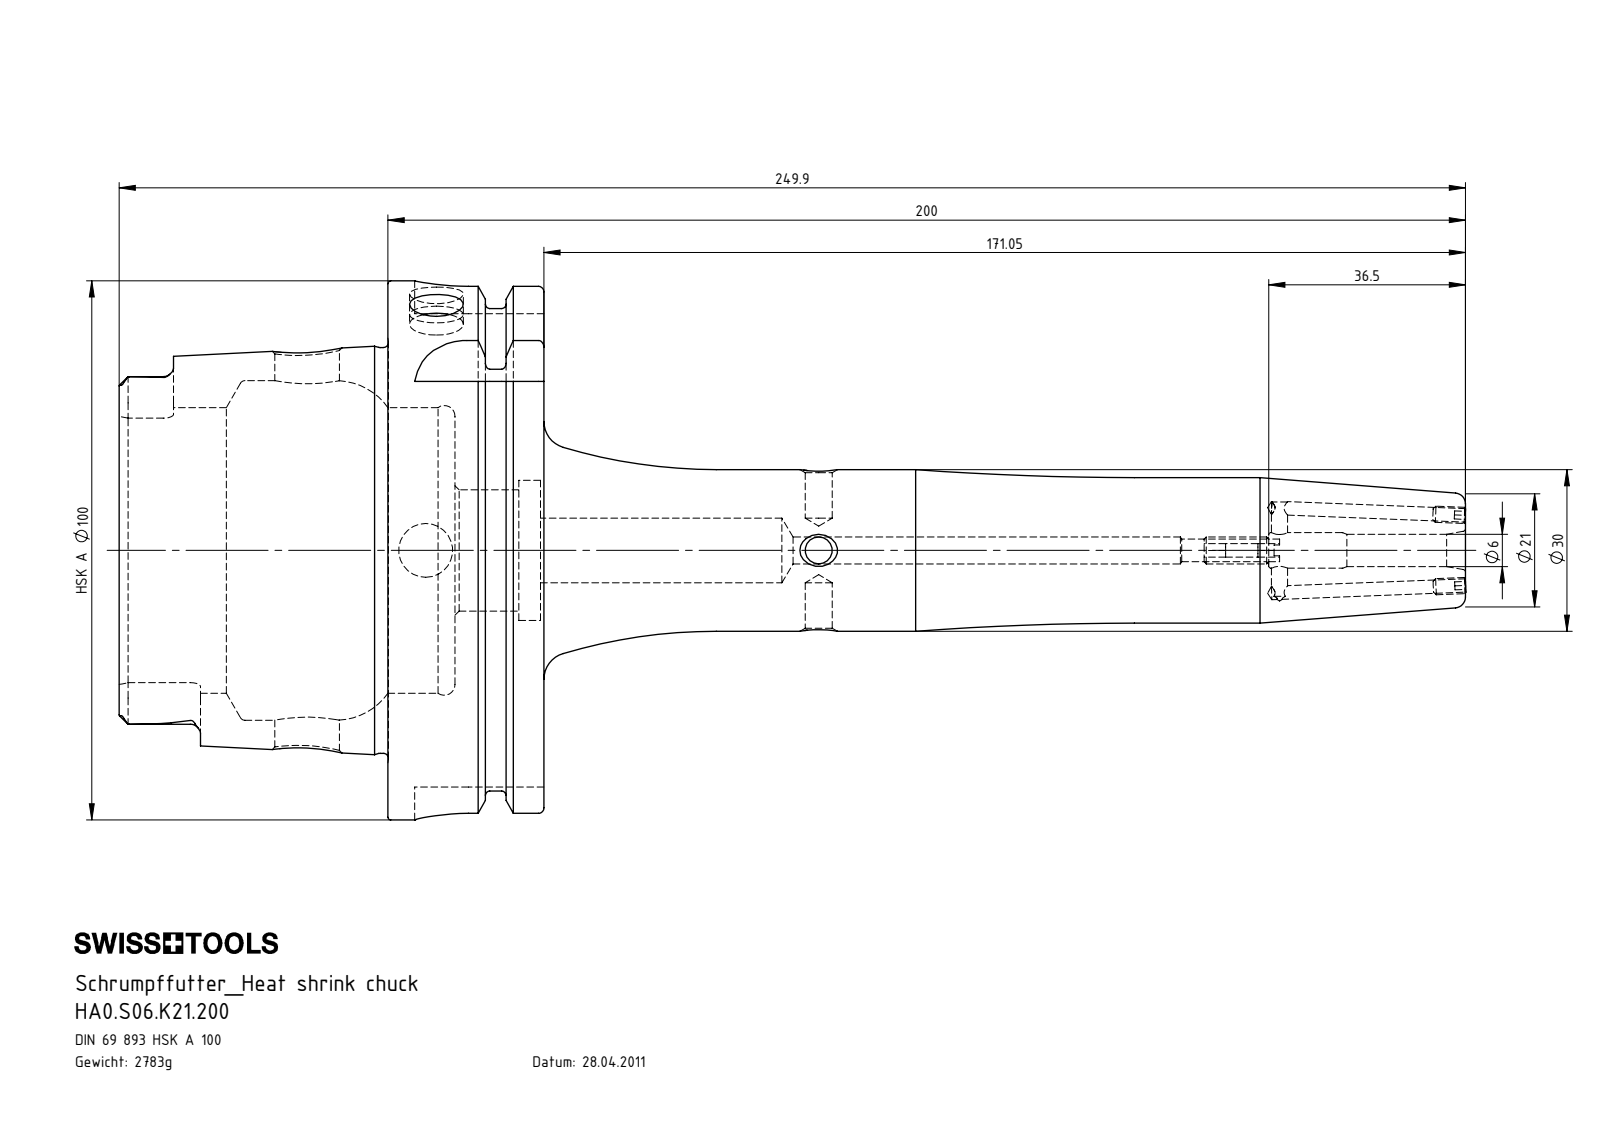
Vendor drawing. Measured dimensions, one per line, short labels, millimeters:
name: ERU-CJ2.001.006; HA0.S06.K21.200; ERU-AN1.K01.014_A; HA0-S06.K21.200_C_Fertigbearbeitung
written by: SolidWorks 2017 (CONFIG_CONTROL_DESIGN)
unit: mm
bodies: 4 solids, 312 faces (95 planar, 93 cylindrical, 124 other)
size: 249.98 × 100 × 100
volume: 354 546 mm³; area: 69 510 mm²
holes: 3× ⌀2.5, 3× ⌀5, 3× ⌀10, 2× ⌀12, 1× ⌀3, 1× ⌀4.2, 1× ⌀6, 1× ⌀6.6, 1× ⌀22.5, 1× ⌀26, 1× ⌀53, 1× ⌀63
bosses: 2× ⌀3, 1× ⌀100, 1× ⌀91.95, 1× ⌀75.26, 1× ⌀30, 1× ⌀27
rounds: 6× R1.9, 4× R4.88, 4× R10
face distances: 28.95, 12.45, 16.5, 49.9, 62.35, 78.85, 87.8, 78.2, 28.3, 15.85
hole spacings: 72.95, 85.55, 94.95, 180.5
